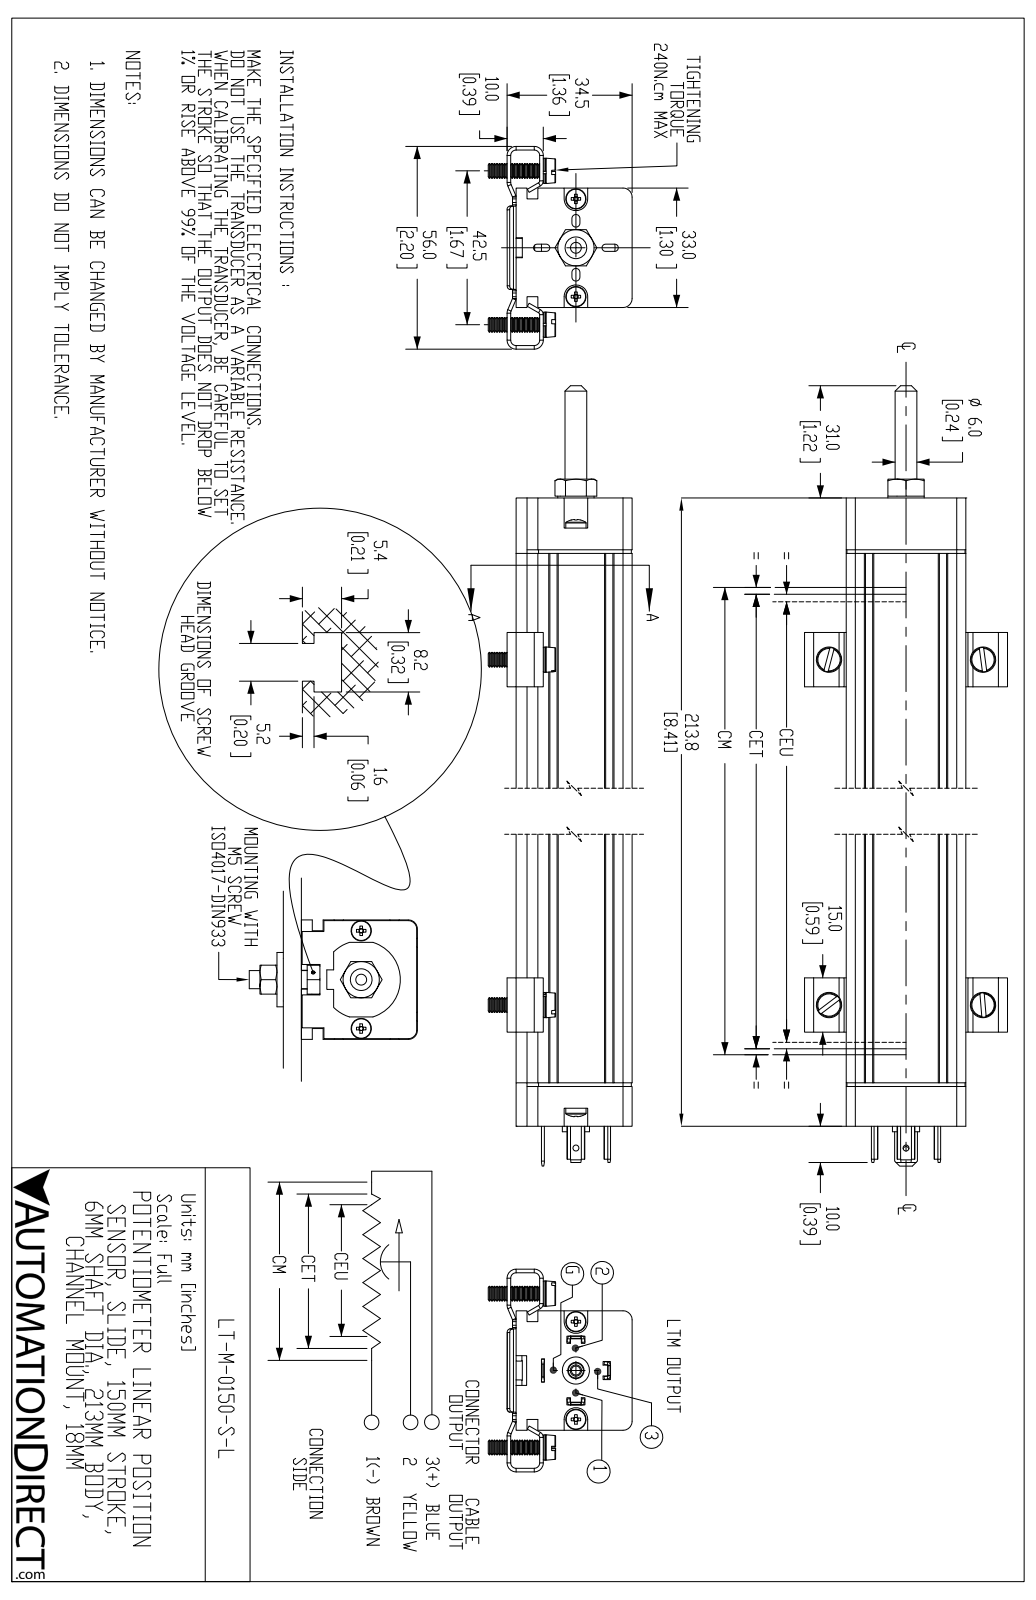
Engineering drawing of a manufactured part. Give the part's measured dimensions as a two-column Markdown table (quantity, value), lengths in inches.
| quantity | value |
| --- | --- |
| part name | LT-M-0150-S-L |
| STEP written by | SolidWorks 2019 (AUTOMOTIVE_DESIGN) |
| units | inches |
| bodies | 21 solids, 1620 faces (696 planar, 356 cylindrical, 568 other) |
| overall size | 10.765 × 2.205 × 1.563 |
| volume | 13.34 in³ |
| surface area | 88.47 in² |
| round holes (diameter × count) | 0.142 × 4, 0.059 × 2, 0.065 × 2, 0.108 × 2, 0.134 × 2, 0.169 × 2, 0.063 × 1, 0.098 × 1, 0.118 × 1, 0.163 × 1, 0.197 × 1, 0.276 × 1 |
| round bosses / shafts (diameter × count) | 0.274 × 4, 0.157 × 4, 0.22 × 2, 0.118 × 2, 0.295 × 1, 0.236 × 1, 0.177 × 1, 0.173 × 1 |
| partial cylindrical surfaces (radius × count) | 0.039 × 34, 0.098 × 12, 0.059 × 10, 0.085 × 8, 0.033 × 6, 0.043 × 4, 0.024 × 2, 0.063 × 2 |
| main face-to-face distances | 1.299, 1.26, 0.118, 0.039, 1.287, 0.213, 0.059, 0.488, 1.024, 1.047 |
| hole center spacings | 0.484, 0.531, 1.359, 1.663, 1.673, 1.766, 1.78, 5.78 |
